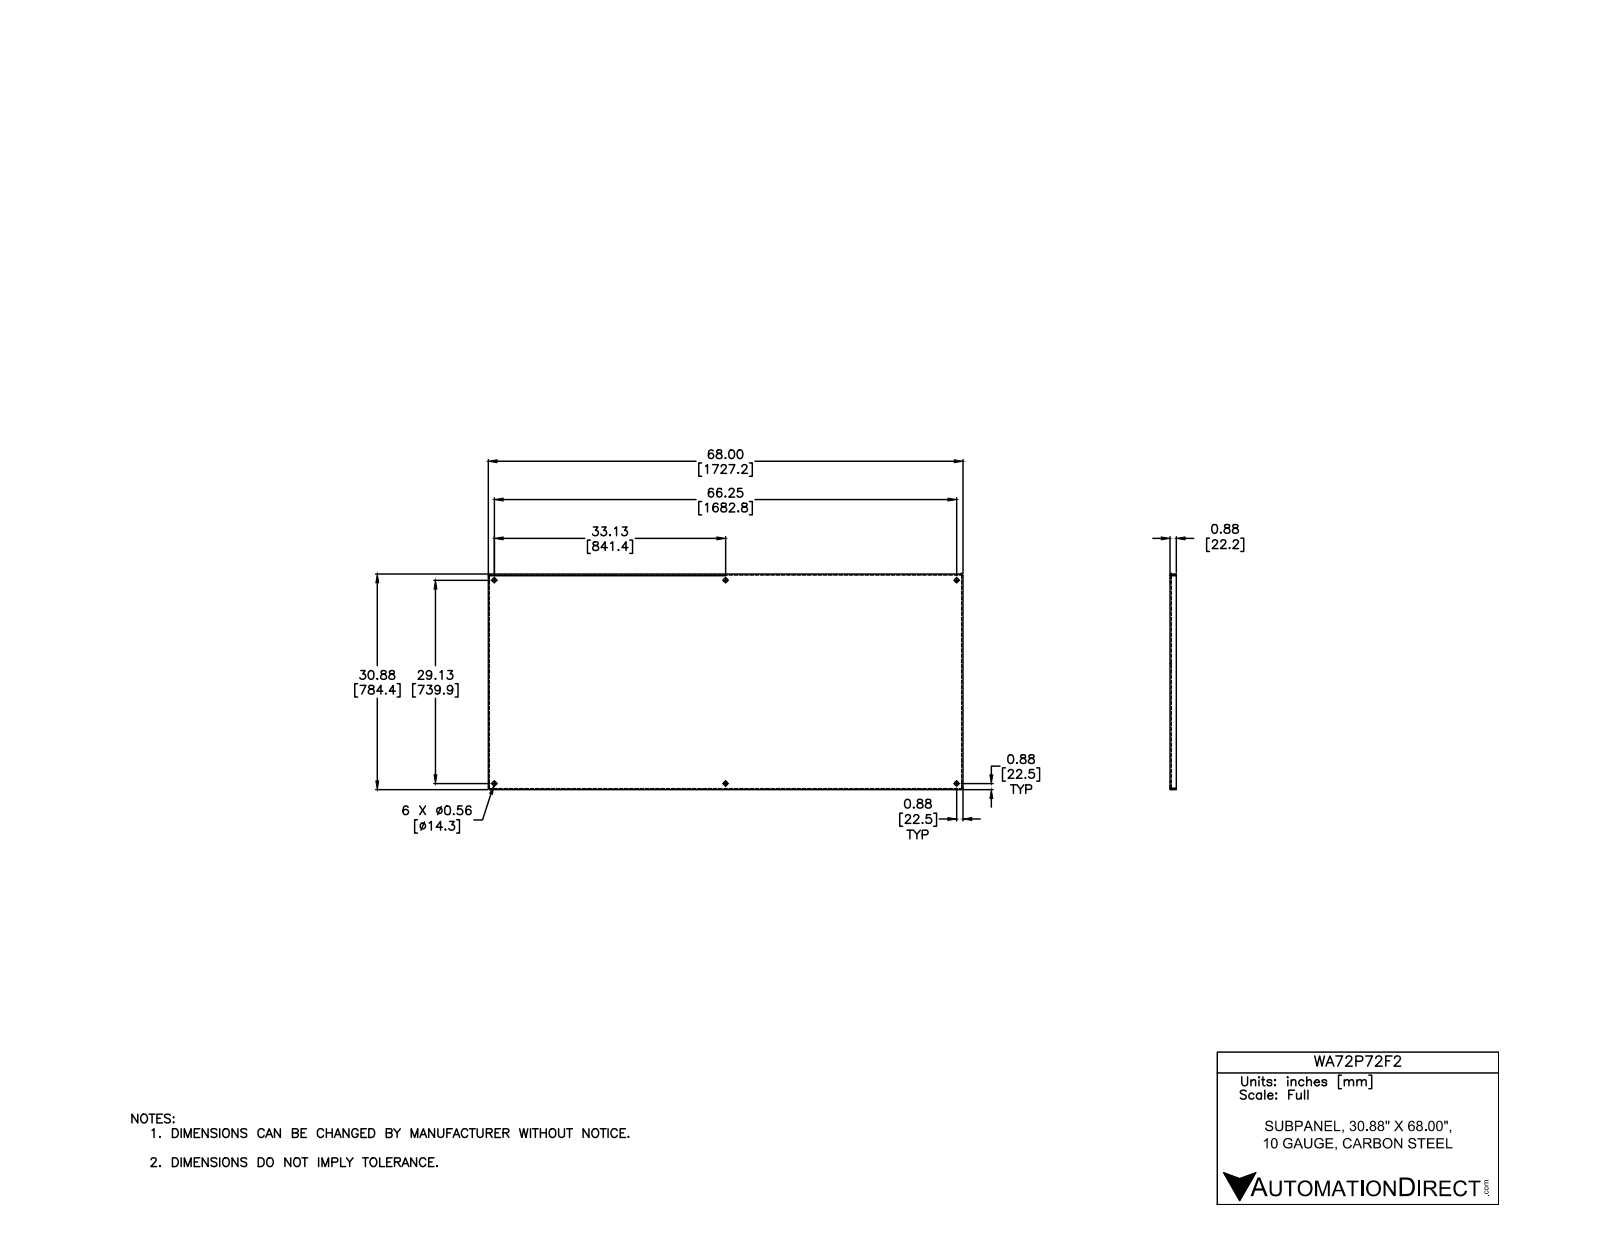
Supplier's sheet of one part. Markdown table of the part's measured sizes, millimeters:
| quantity | value |
| --- | --- |
| part name | WA_P_F |
| STEP written by | Autodesk Inventor 2012 (AUTOMOTIVE_DESIGN) |
| units | millimeters |
| bodies | 1 solid, 44 faces (22 planar, 14 cylindrical, 8 other) |
| overall size | 1727.2 × 784.4 × 22.2 |
| volume | 4 583 000 mm³ |
| surface area | 2 904 000 mm² |
| round holes (diameter × count) | 14.3 × 6 |
| partial cylindrical surfaces (radius × count) | 0.8 × 4, 4 × 4 |
| main face-to-face distances | 3.2, 3.2, 781.2, 784.4, 778, 781.2, 1724, 19.1, 22.2, 1727.2 |
| hole center spacings | 1120.4, 739.9, 841.4, 841.4, 1682.8, 1682.8, 1838.2, 1838.2 |
